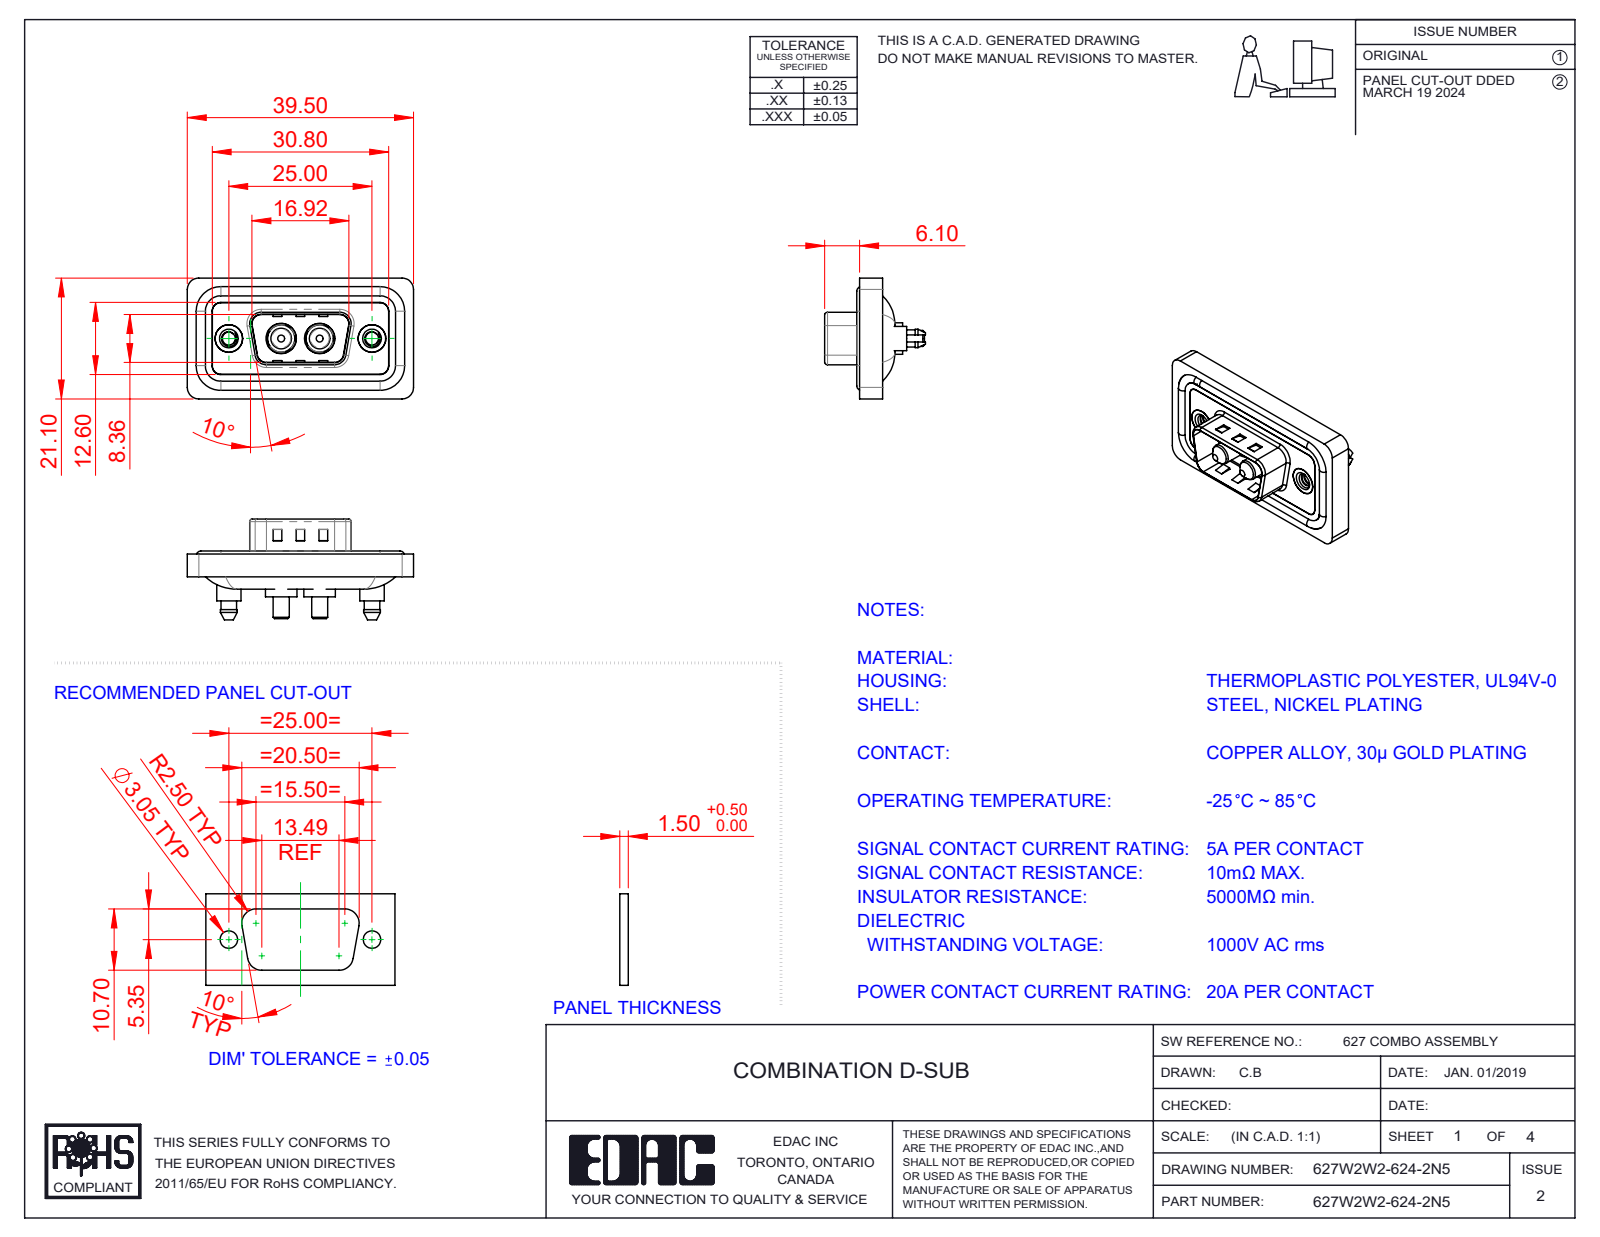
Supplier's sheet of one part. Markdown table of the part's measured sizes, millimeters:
| quantity | value |
| --- | --- |
| part name | 627Combo Shell Front_09 Contacts; 627Combo Housing_2W2; Power Pin_20A S; 627W2W2-624-2N5 (+3 more) |
| STEP written by | SolidWorks 2023 (CONFIG_CONTROL_DESIGN) |
| units | millimeters |
| bodies | 11 solids, 539 faces (181 planar, 250 cylindrical, 108 other) |
| overall size | 39.5 × 21.1 × 17.6 |
| volume | 4 594 mm³ |
| surface area | 7 317 mm² |
| round holes (diameter × count) | 2.26 × 2, 4 × 2, 4.8 × 2, 4.85 × 2, 5 × 2, 5.3 × 2 |
| round bosses / shafts (diameter × count) | 1.6 × 4, 5.5 × 2, 5.4 × 2, 5.2 × 2, 4.9 × 2, 4.75 × 2, 4.25 × 2, 3.75 × 2 |
| partial cylindrical surfaces (radius × count) | 1.5 × 24, 2 × 18, 1.6 × 10, 0.5 × 8, 0.25 × 4, 0.6 × 4, 0.65 × 4, 0.9 × 4 |
| main face-to-face distances | 0.4, 1.1, 2.9, 3.1, 0.5, 1.6, 1.5, 4, 0.7, 2.5 |
| hole center spacings | 9.14, 15.86, 6.72, 25 |
